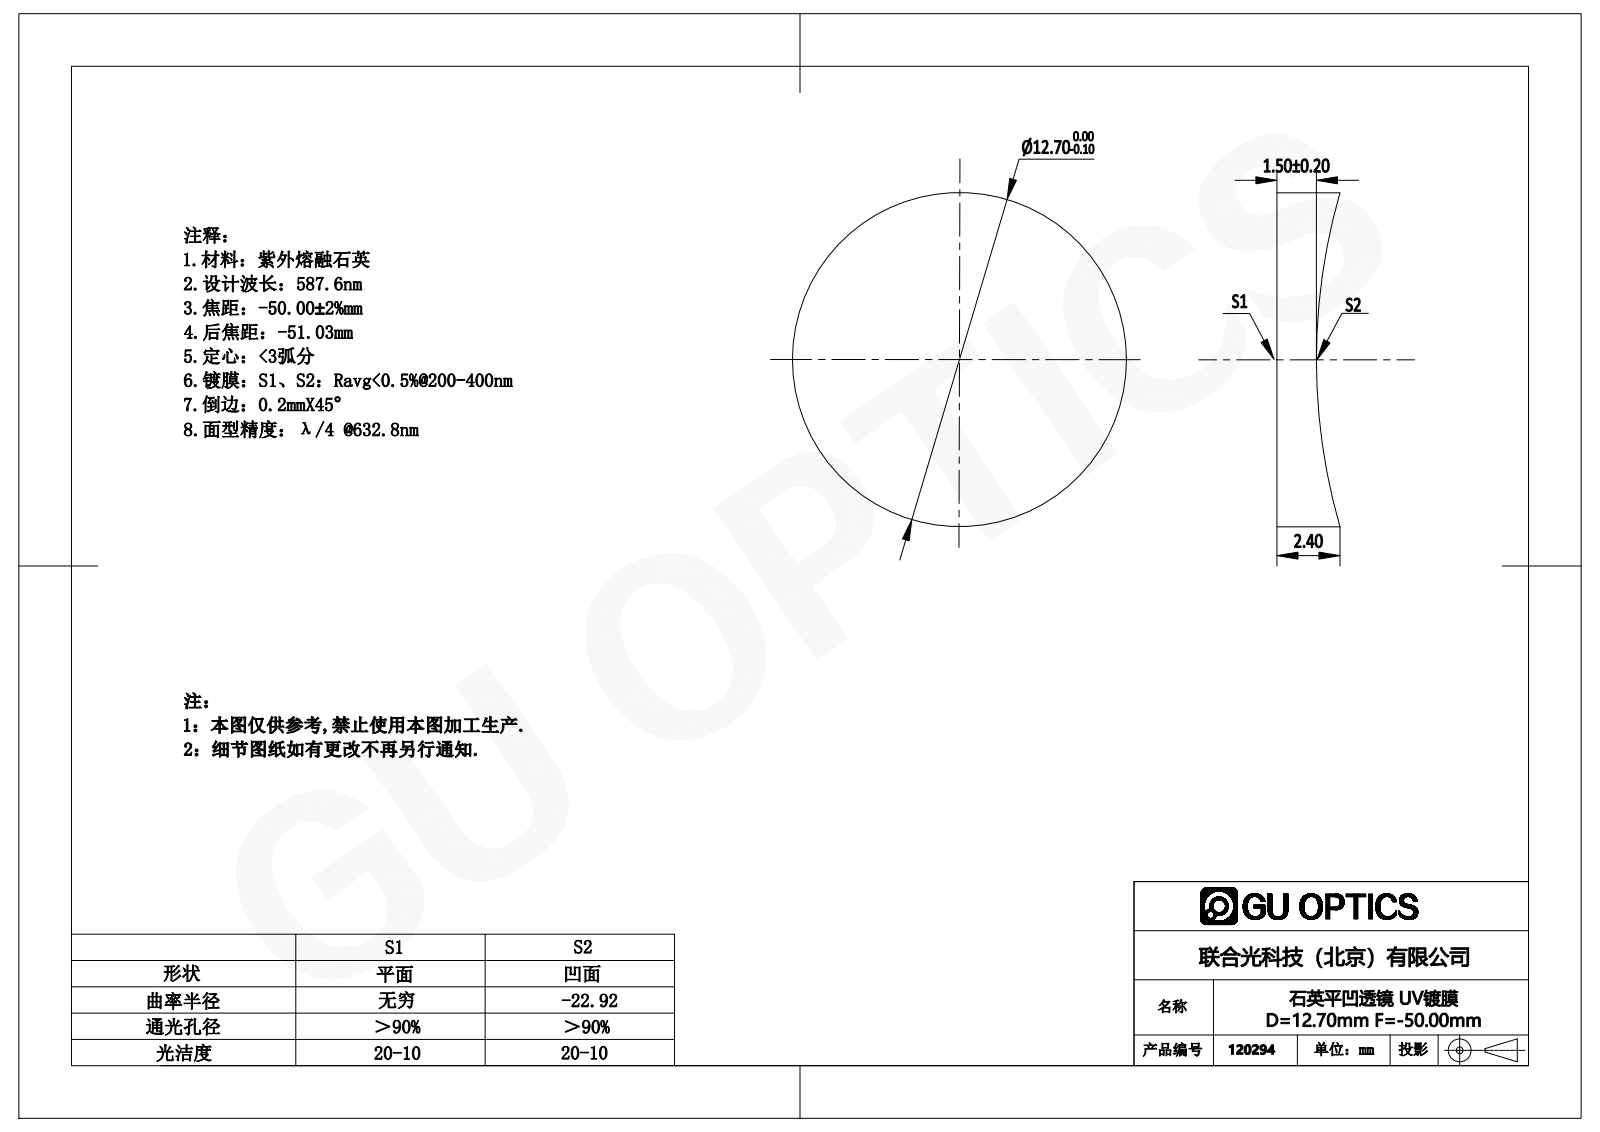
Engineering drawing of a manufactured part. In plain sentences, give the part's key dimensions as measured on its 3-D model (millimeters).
The part is named "120261". Its 3-D file was written by "SolidWorks 2016 (AUTOMOTIVE_DESIGN)". It is 1 solid with 5 faces: 1 planar, 2 cylindrical and 2 other. Overall it measures 12.7 by 12.7 by 2.4 millimeters. Its volume is 246 cubic millimeters and its surface area 352 square millimeters. Round bosses or shafts: 1 of diameter 12.7.
